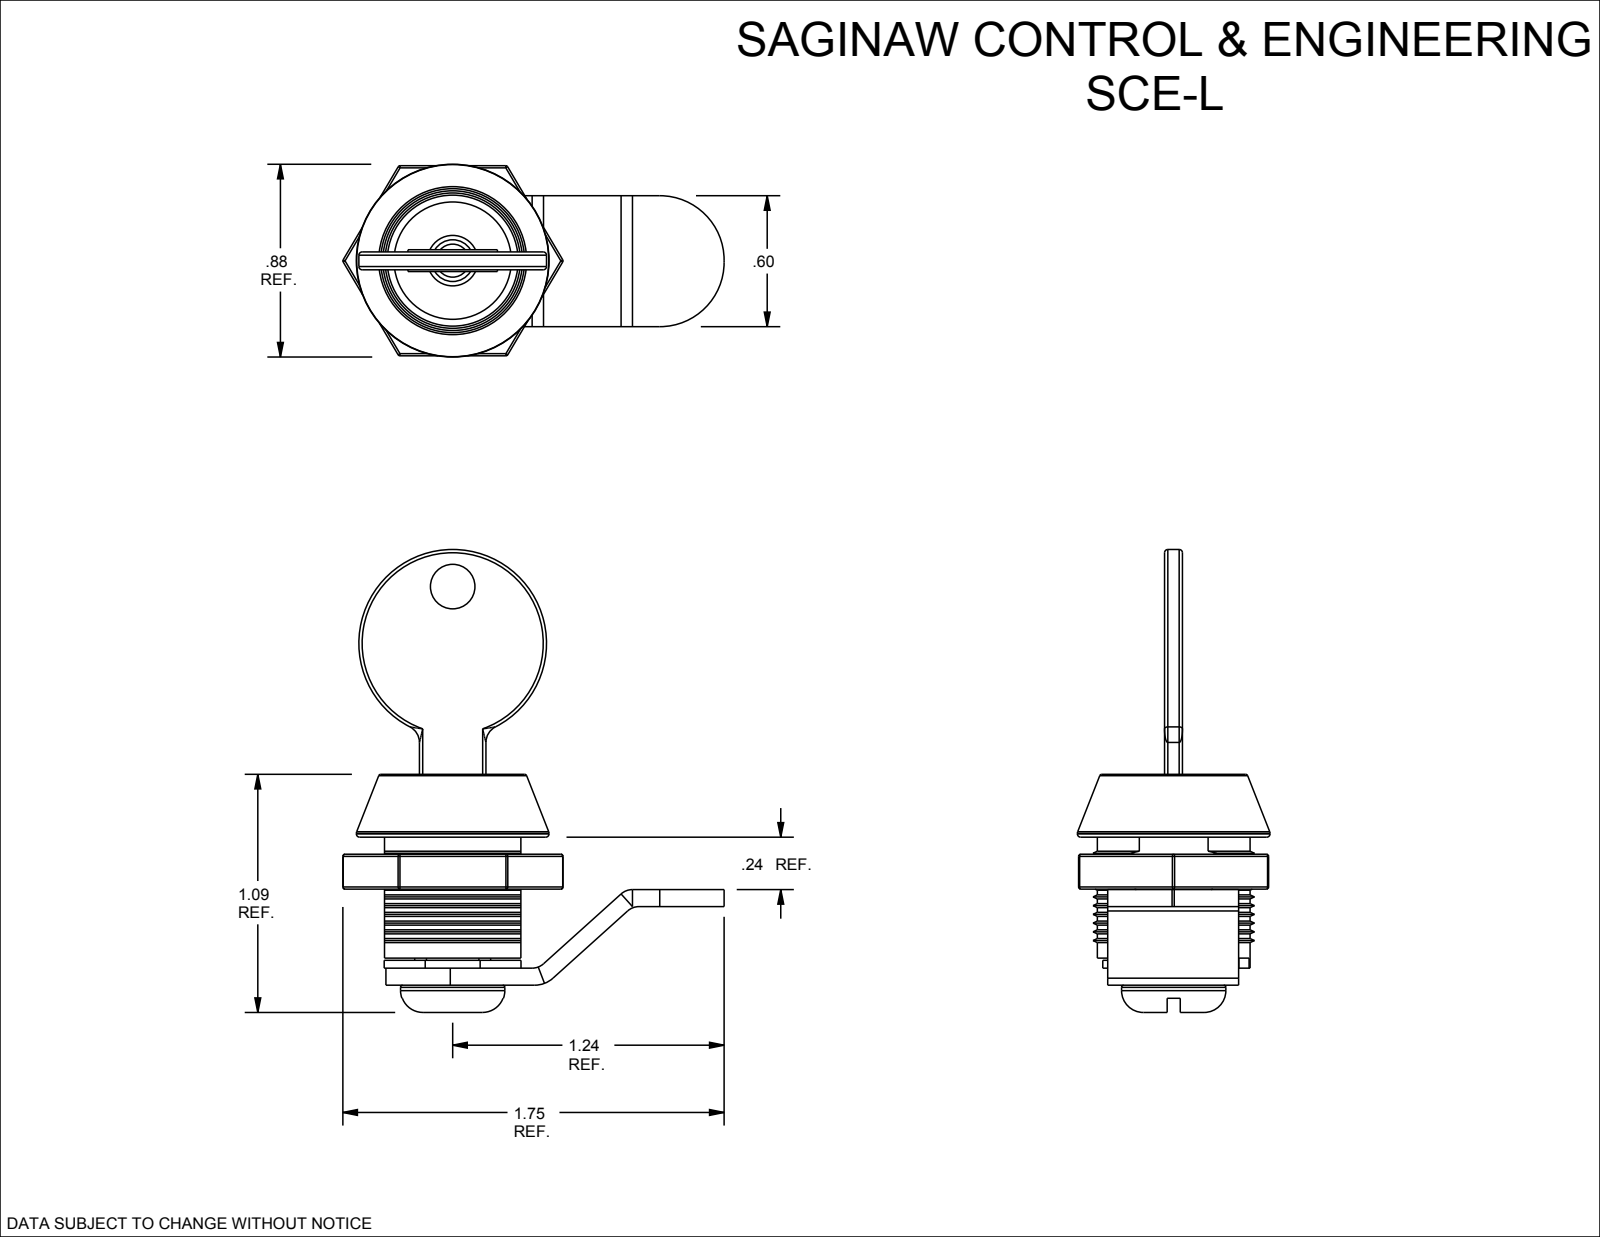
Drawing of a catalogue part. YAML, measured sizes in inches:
part_name: "SCE-L"
step_written_by: "SolidWorks 2019 (CONFIG_CONTROL_DESIGN)"
units: inches
bodies: {solids: 7, faces: 283, planar: 101, cylindrical: 105, other: 77}
overall_size: [2.121, 1.747, 0.883]
volume: 0.54
surface_area: 13.38
round_holes:
  - {diameter: 0.204, count: 1}
  - {diameter: 0.206, count: 1}
  - {diameter: 0.5, count: 1}
  - {diameter: 0.62, count: 1}
  - {diameter: 0.709, count: 1}
round_bosses_or_shafts:
  - {diameter: 0.883, count: 1}
  - {diameter: 0.86, count: 1}
  - {diameter: 0.6, count: 1}
  - {diameter: 0.478, count: 1}
  - {diameter: 0.423, count: 1}
  - {diameter: 0.19, count: 1}
partial_cylinders:
  - {radius: 0.015, count: 28}
  - {radius: 0.01, count: 18}
  - {radius: 0.03, count: 4}
  - {radius: 0.295, count: 4}
  - {radius: 0.078, count: 3}
  - {radius: 0.08, count: 2}
  - {radius: 0.096, count: 1}
  - {radius: 0.125, count: 1}
face_to_face_distances: [0.078, 0.082, 0.6, 0.36, 0.24, 0.078, 0.08, 0.486, 0.476, 0.124]
